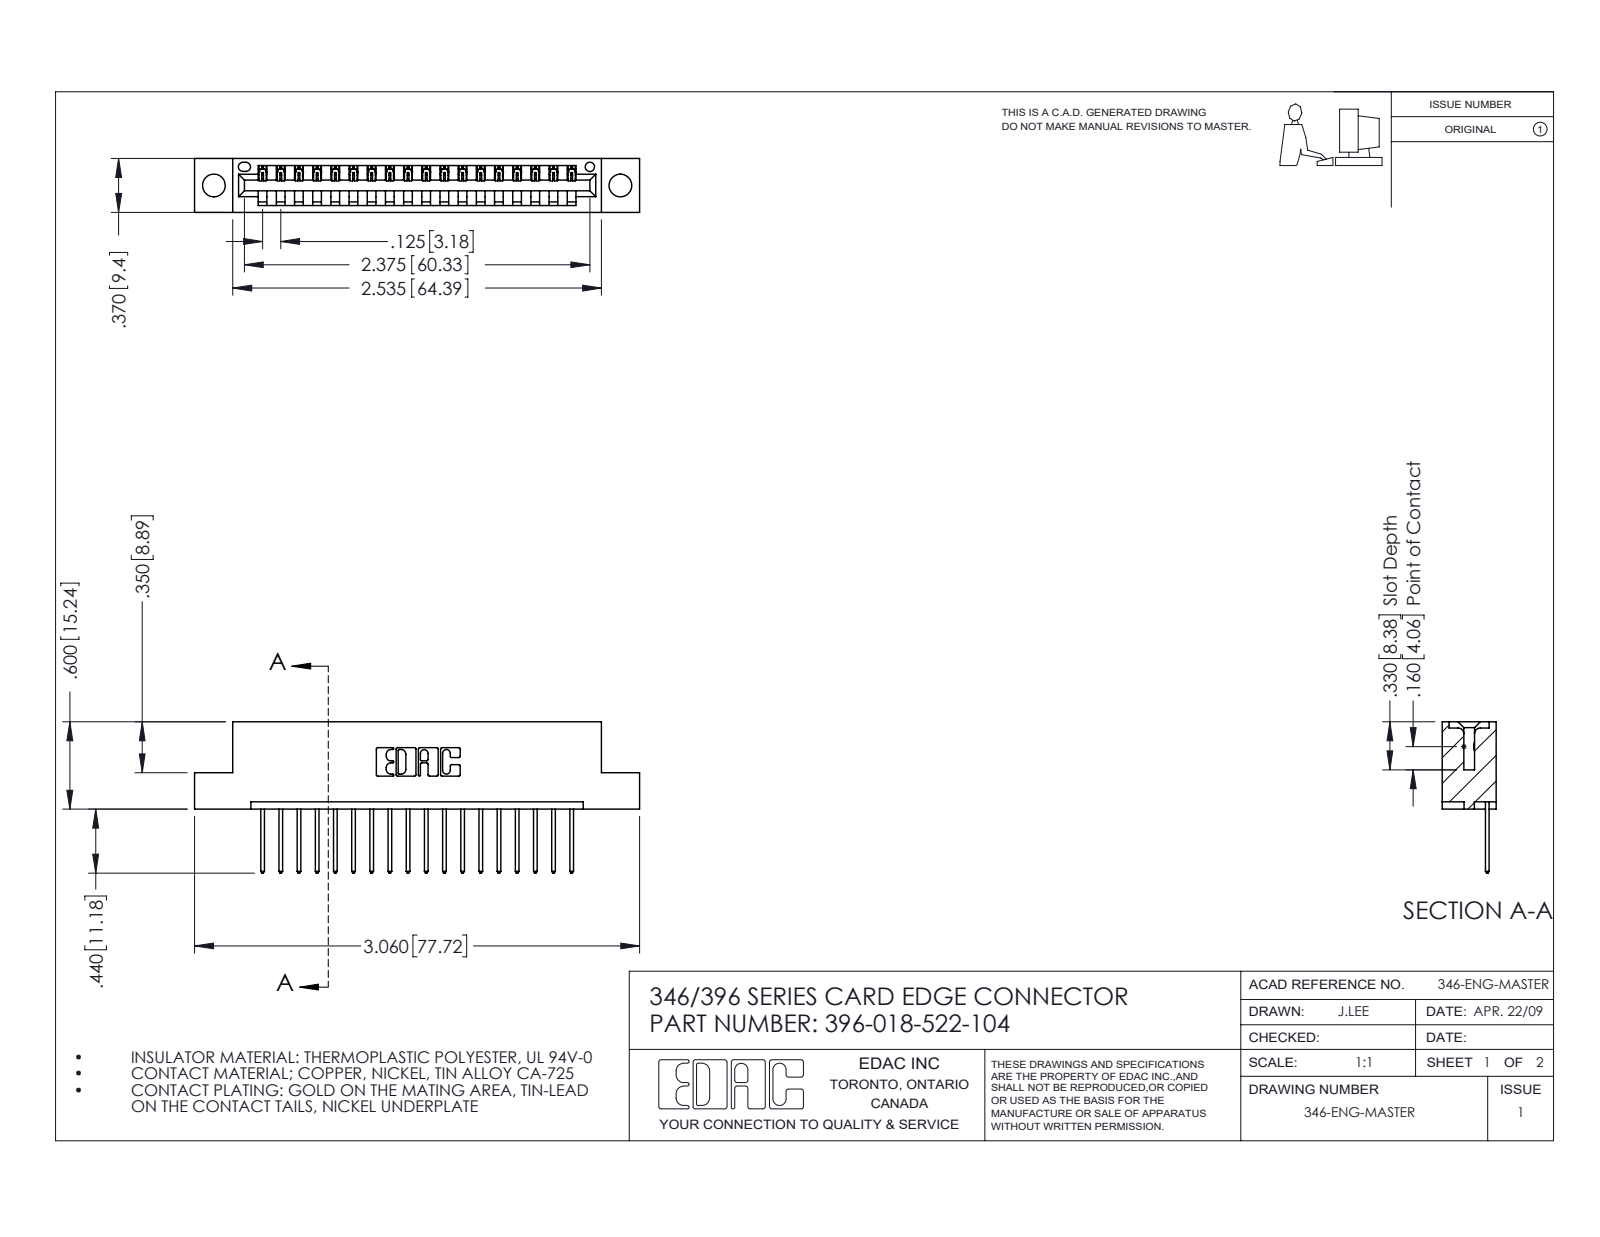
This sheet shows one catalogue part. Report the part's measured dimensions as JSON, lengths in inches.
{"part_name": "346 Part_Flush Mounting Lugs - 0.156 Dia-TH; 345-292-001_345-293-122; 396-018-522-104", "step_written_by": "SolidWorks 2016 (CONFIG_CONTROL_DESIGN)", "units": "inches", "bodies": {"solids": 19, "faces": 1166, "planar": 796, "cylindrical": 370, "other": 0}, "overall_size": [3.06, 1.04, 0.37], "volume_in3": 0.439, "surface_area_in2": 13.33, "round_holes": [[0.156, 2], [0.064, 1]], "partial_cylinders_radius": [[0.006, 36], [0.01, 36], [0.01, 22], [0.007, 6], [0.031, 6], [0.026, 3], [0.031, 2], [0.04, 2]], "face_to_face_distances": [0.048, 0.322, 0.25, 0.37, 0.072, 0.298, 0.025, 0.148, 0.222, 0.1], "hole_center_spacings": [0.246, 2.588, 2.795]}
